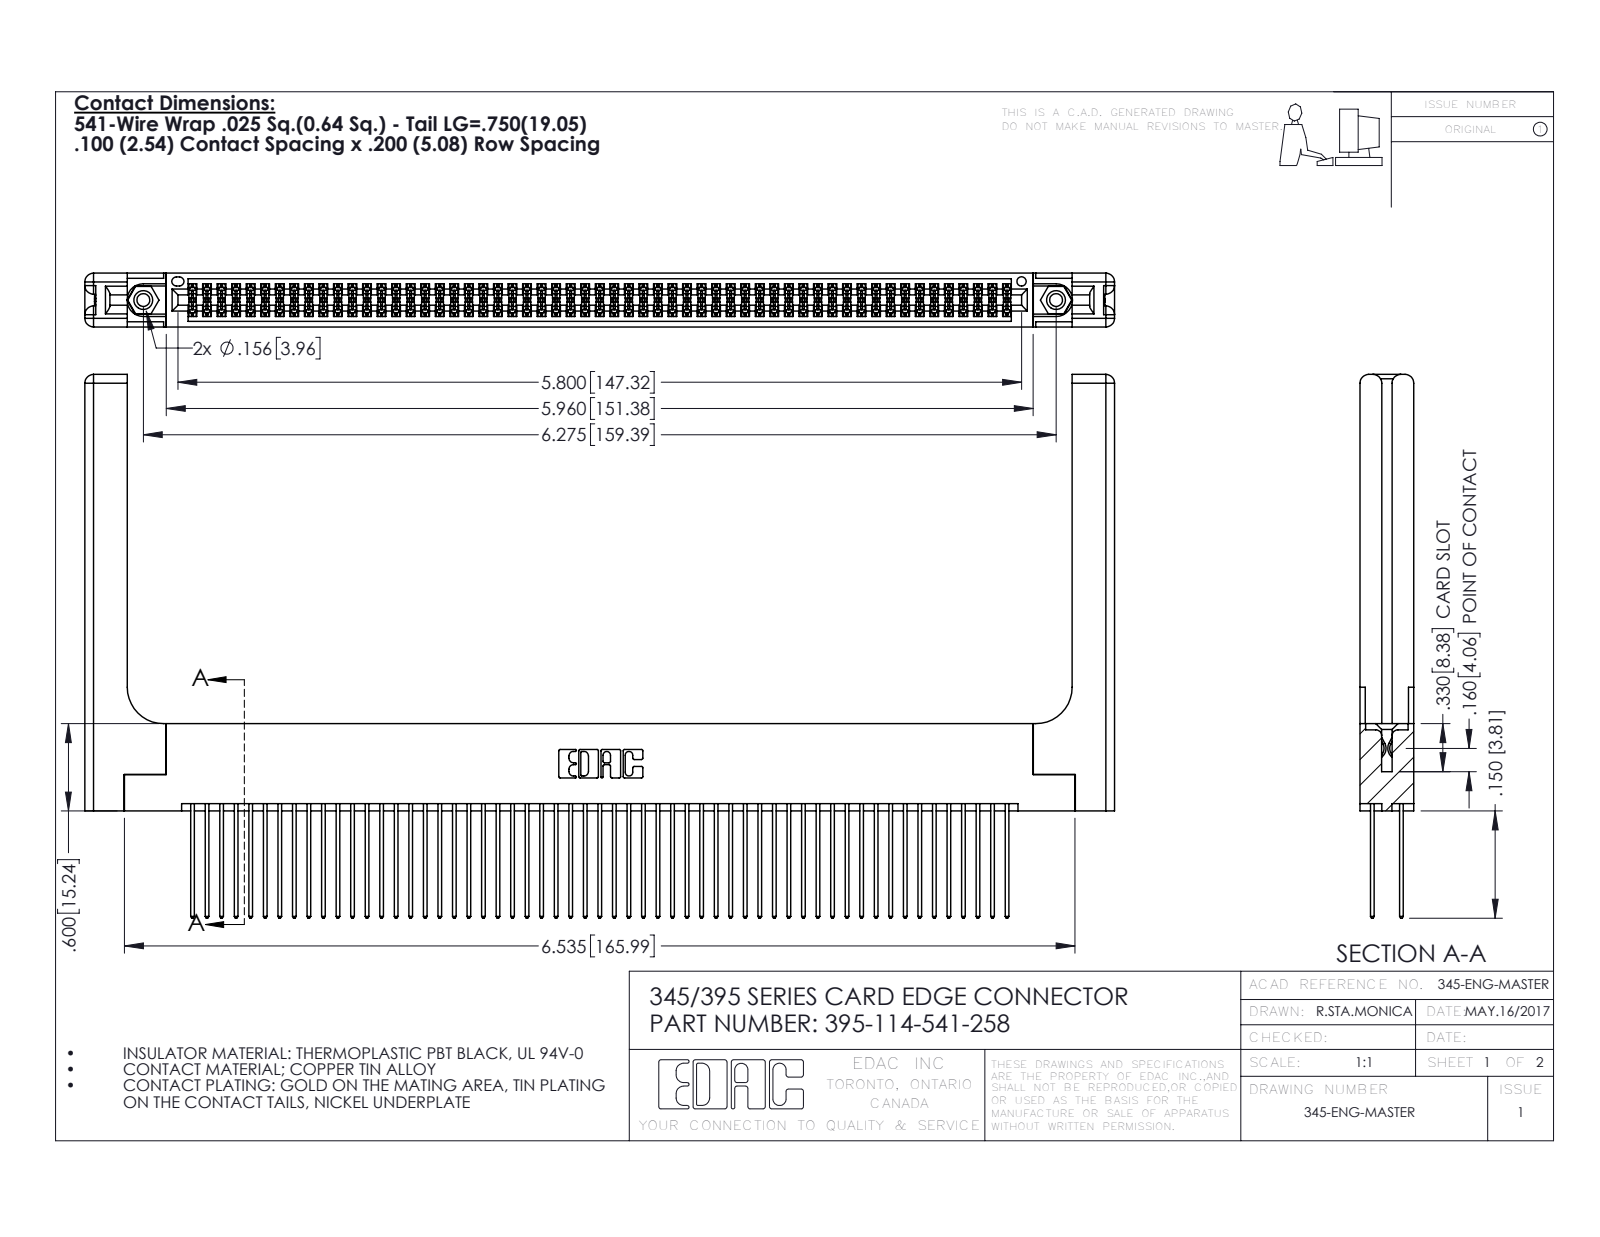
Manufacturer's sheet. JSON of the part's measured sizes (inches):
{"part_name": "345 Part_Flush Mounting Lugs - 0.156 Dia-TH; 345-250-001_345-250-001-102; 345-292-001_345-293-141; 395-114-541-258 (+1 more)", "step_written_by": "SolidWorks 2016 (CONFIG_CONTROL_DESIGN)", "units": "inches", "bodies": {"solids": 119, "faces": 6082, "planar": 3990, "cylindrical": 2032, "other": 60}, "overall_size": [7.079, 3.737, 0.37], "volume_in3": 1.631, "surface_area_in2": 54.89, "round_holes": [[0.089, 2], [0.125, 2], [0.156, 2], [0.064, 1]], "round_bosses_or_shafts": [[0.155, 2]], "partial_cylinders_radius": [[0.006, 171], [0.01, 114], [0.01, 22], [0.06, 16], [0.007, 6], [0.031, 6], [0.026, 3], [0.014, 2]], "face_to_face_distances": [0.072, 0.298, 0.2, 0.098, 0.272, 0.025, 0.37, 0.225, 0.175, 0.148], "hole_center_spacings": [0.27, 6.039, 6.275]}
